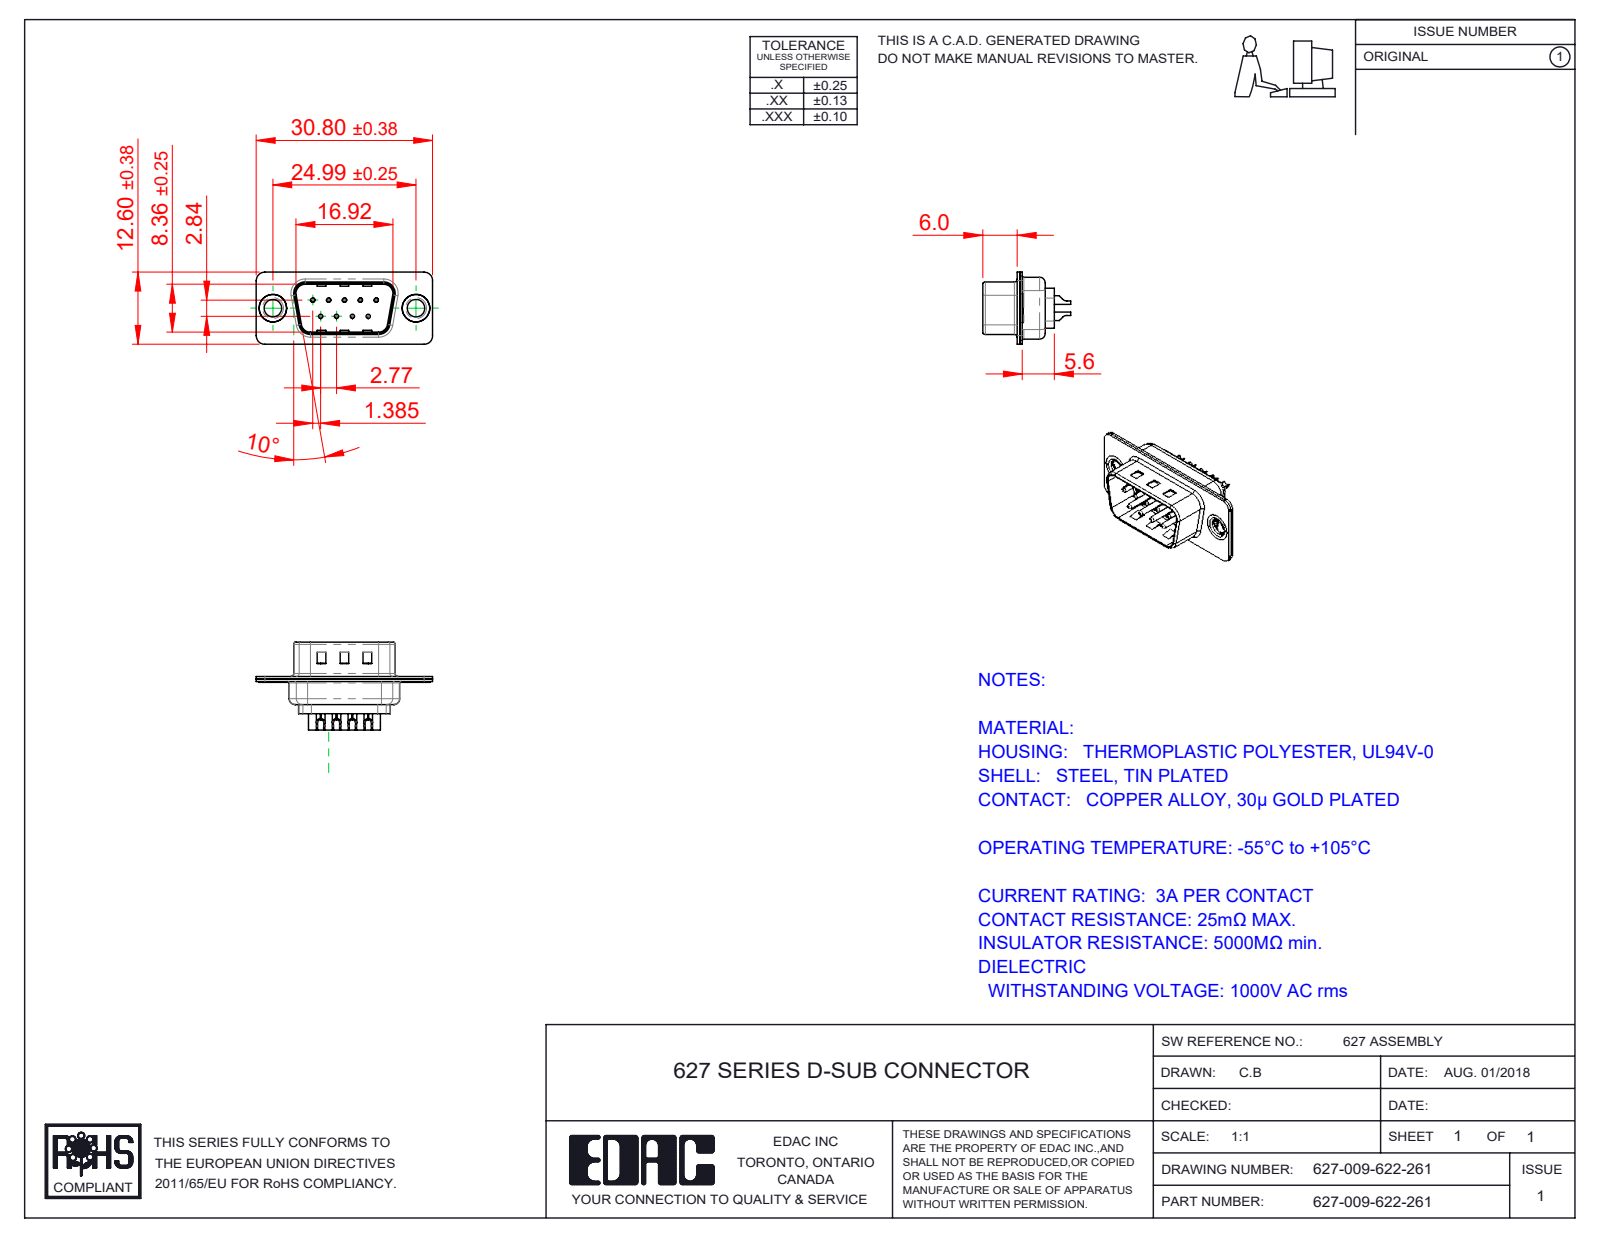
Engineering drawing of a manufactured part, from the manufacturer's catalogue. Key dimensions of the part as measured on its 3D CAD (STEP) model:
Part name (STEP PRODUCT): 627 Shell Front_09 Contacts; 627-009-622-061; 627 Contact Row 2_22L; 627 Thru Hole Rivet (+3 more)
STEP written by: SolidWorks 2020 (CONFIG_CONTROL_DESIGN)
Units: millimetres
Bodies: 14 solids, 854 faces (233 planar, 374 cylindrical, 247 other)
Overall size (bounding box): 30.8 × 15.35 × 12.6
Volume: 1 237 mm³ · Surface area: 3 808 mm²
Round holes (diameter × count): ⌀0.35 ×9, ⌀1.1 ×9, ⌀1.6 ×9, ⌀3.05 ×2, ⌀4 ×2, ⌀4.8 ×2
Round bosses / shafts (diameter × count): ⌀2 ×9, ⌀1.5 ×9, ⌀0.75 ×9, ⌀5 ×2, ⌀4.9 ×2, ⌀3.55 ×2
Partial cylindrical surfaces — rounded edges, fillets, slot ends (radius × count): R1.5 ×18, R2 ×12, R0.5 ×8, R1.6 ×8, R1 ×6, R0.25 ×4, R0.6 ×4, R0.65 ×4
Main face-to-face distances: 0.45, 0.4, 0.9, 0.82, 9.58, 1.4, 0.5, 8.76, 1.5, 6.5
Hole centre spacings: 3.16, 2.77, 5.54, 5.03, 5.04, 8.31, 7.48, 7.49
